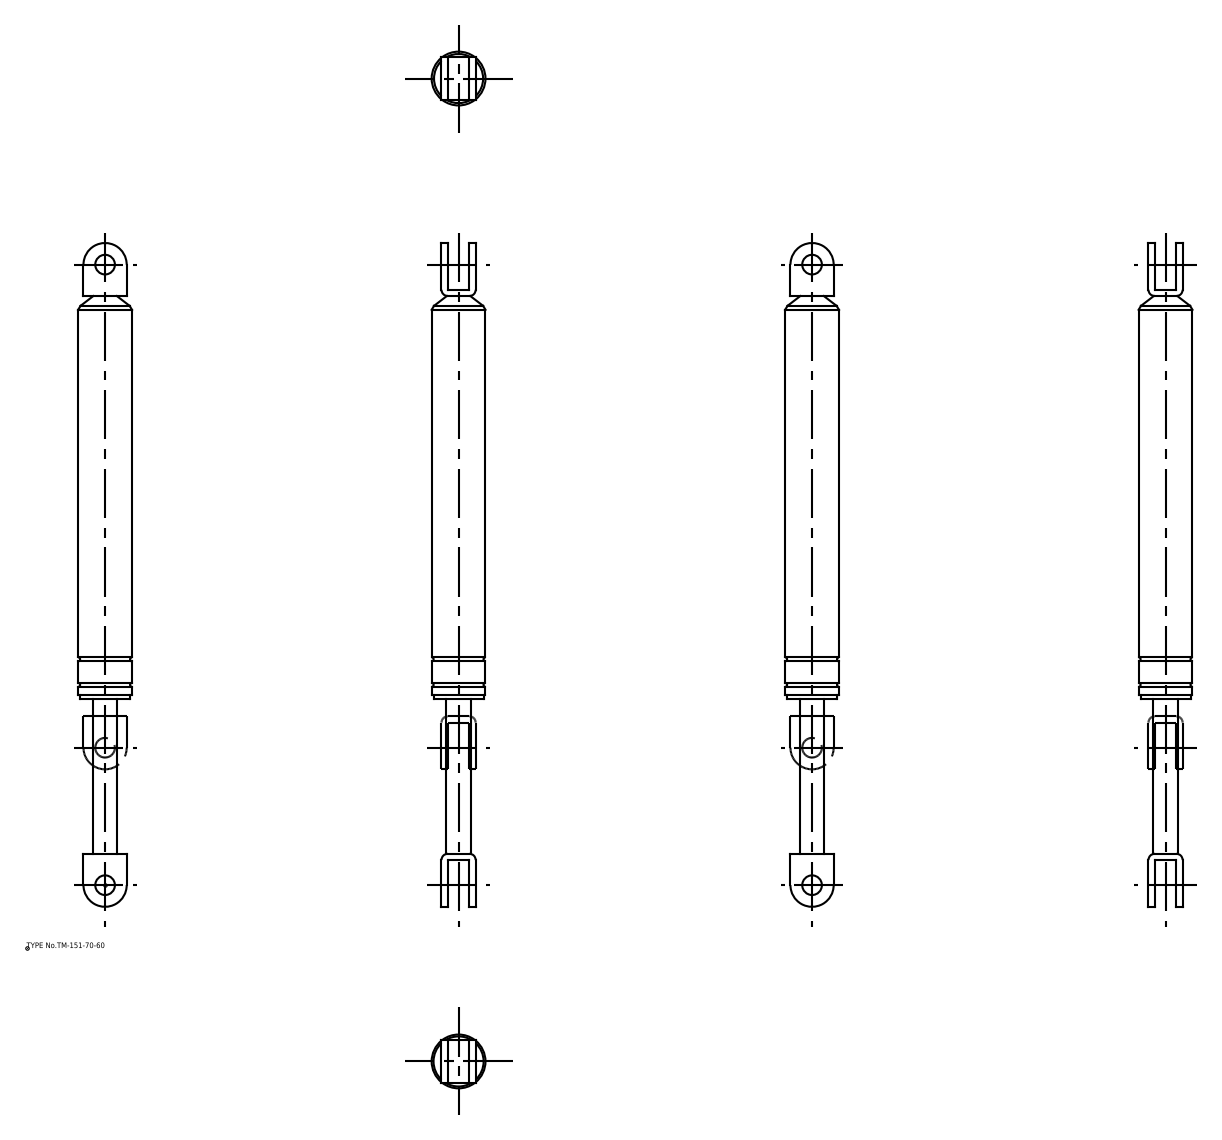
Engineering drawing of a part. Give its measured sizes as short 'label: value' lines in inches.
name: TM_151_70_60; TM_151_70_60_div
written by: spGate 16.7.1 (AUTOMOTIVE_DESIGN)
unit: in
bodies: 2 solids, 64 faces (22 planar, 32 cylindrical, 10 other)
size: 13.307 × 1.11 × 1.11
volume: 8.315 in³; area: 42.67 in²
holes: 2× ⌀0.394
bosses: 1× ⌀1.11, 1× ⌀1.079, 1× ⌀1.004, 1× ⌀0.492
rounds: 4× R0.126, 2× R0.433
face distances: 0.126, 0.559, 0.685, 0.433, 0.866, 11.307, 3.236, 11.433, 8.197, 8.071
hole spacings: 12.441
